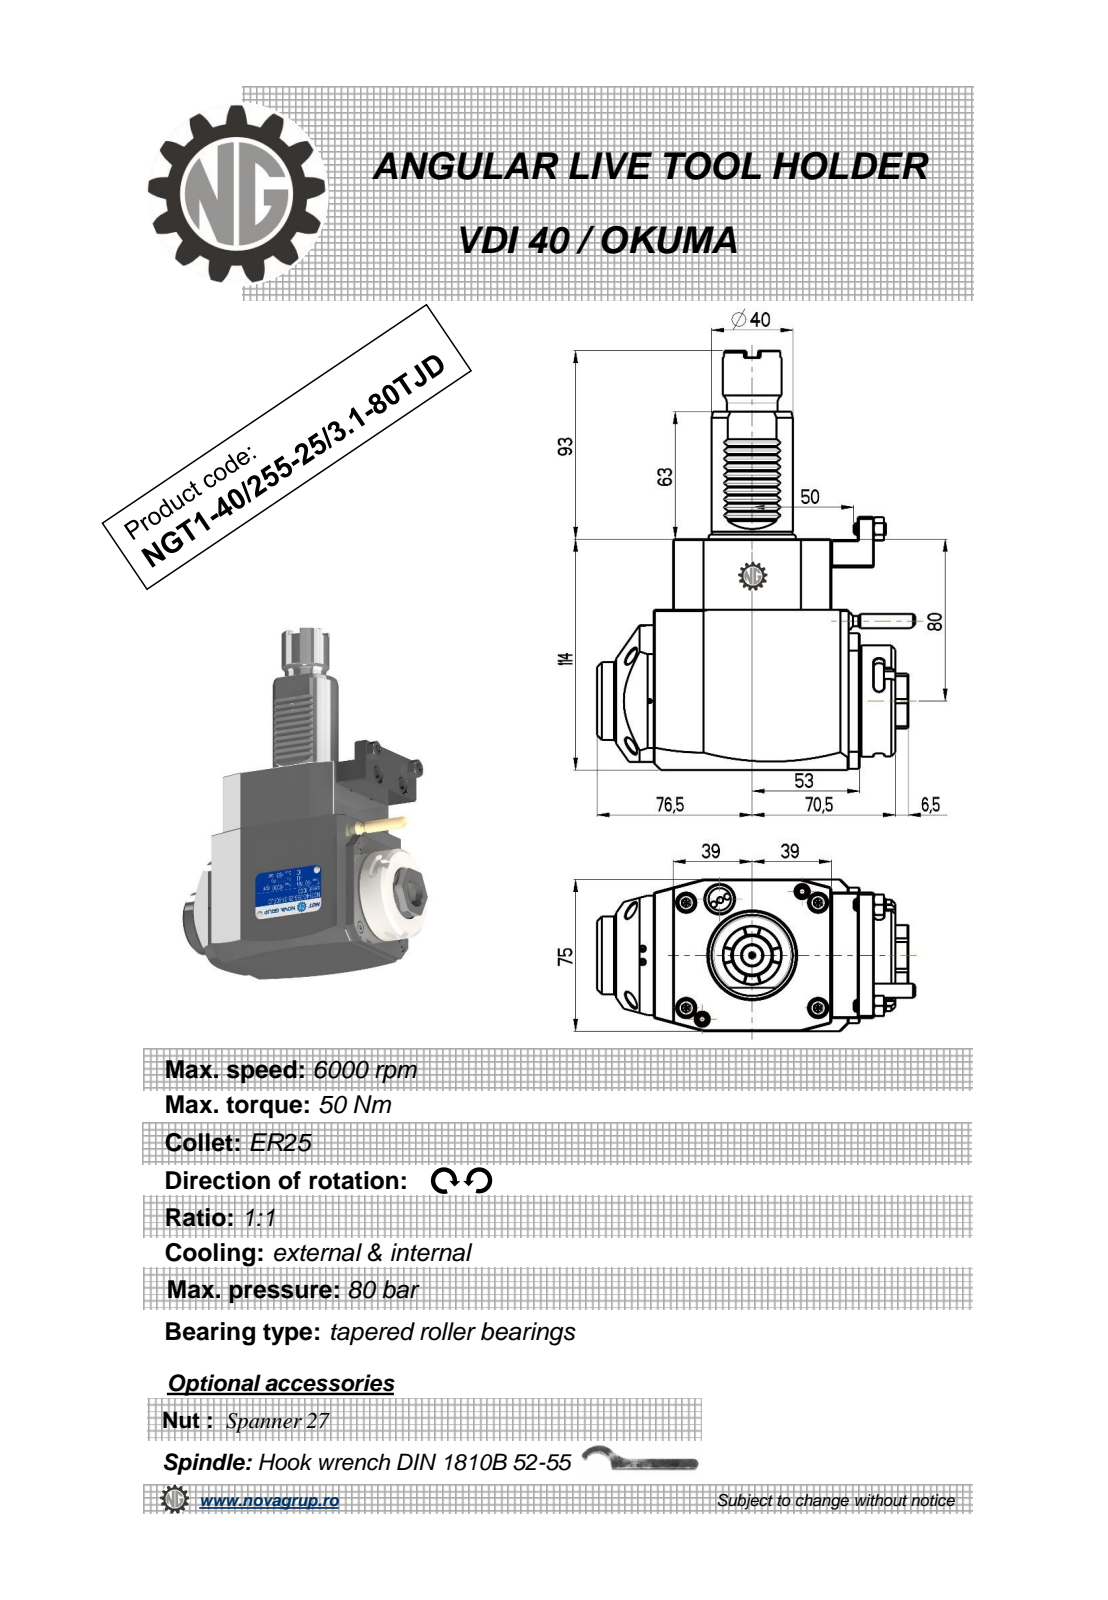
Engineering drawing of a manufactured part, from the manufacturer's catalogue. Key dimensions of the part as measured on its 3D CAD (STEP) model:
Part name (STEP PRODUCT): NGT1_40_255_25_3_1_80TJD
STEP written by: PRO/ENGINEER BY PARAMETRIC TECHNOLOGY CORPORATION, 2010280 (CONFIG_CONTROL_DESIGN)
Units: millimetres
Bodies: 1 solid, 402 faces (194 planar, 78 cylindrical, 130 other)
Overall size (bounding box): 207 × 156.83 × 75
Volume: 999 586 mm³ · Surface area: 76 315 mm²
Round holes (diameter × count): ⌀2.5 ×1, ⌀3 ×1, ⌀18 ×1
Round bosses / shafts (diameter × count): ⌀6 ×2, ⌀55 ×1, ⌀48 ×1, ⌀40 ×1, ⌀38.5 ×1, ⌀29 ×1, ⌀25 ×1, ⌀8.96 ×1
Partial cylindrical surfaces — rounded edges, fillets, slot ends (radius × count): R0.3 ×10, R0.31 ×10, R2.5 ×6, R180 ×2, R0.5 ×1, R10 ×1, R15 ×1, R24.5 ×1
Main face-to-face distances: 75, 114, 14, 21, 109.5, 92, 17.5, 0.5, 31.5, 6.5
Hole centre spacings: 43.2
